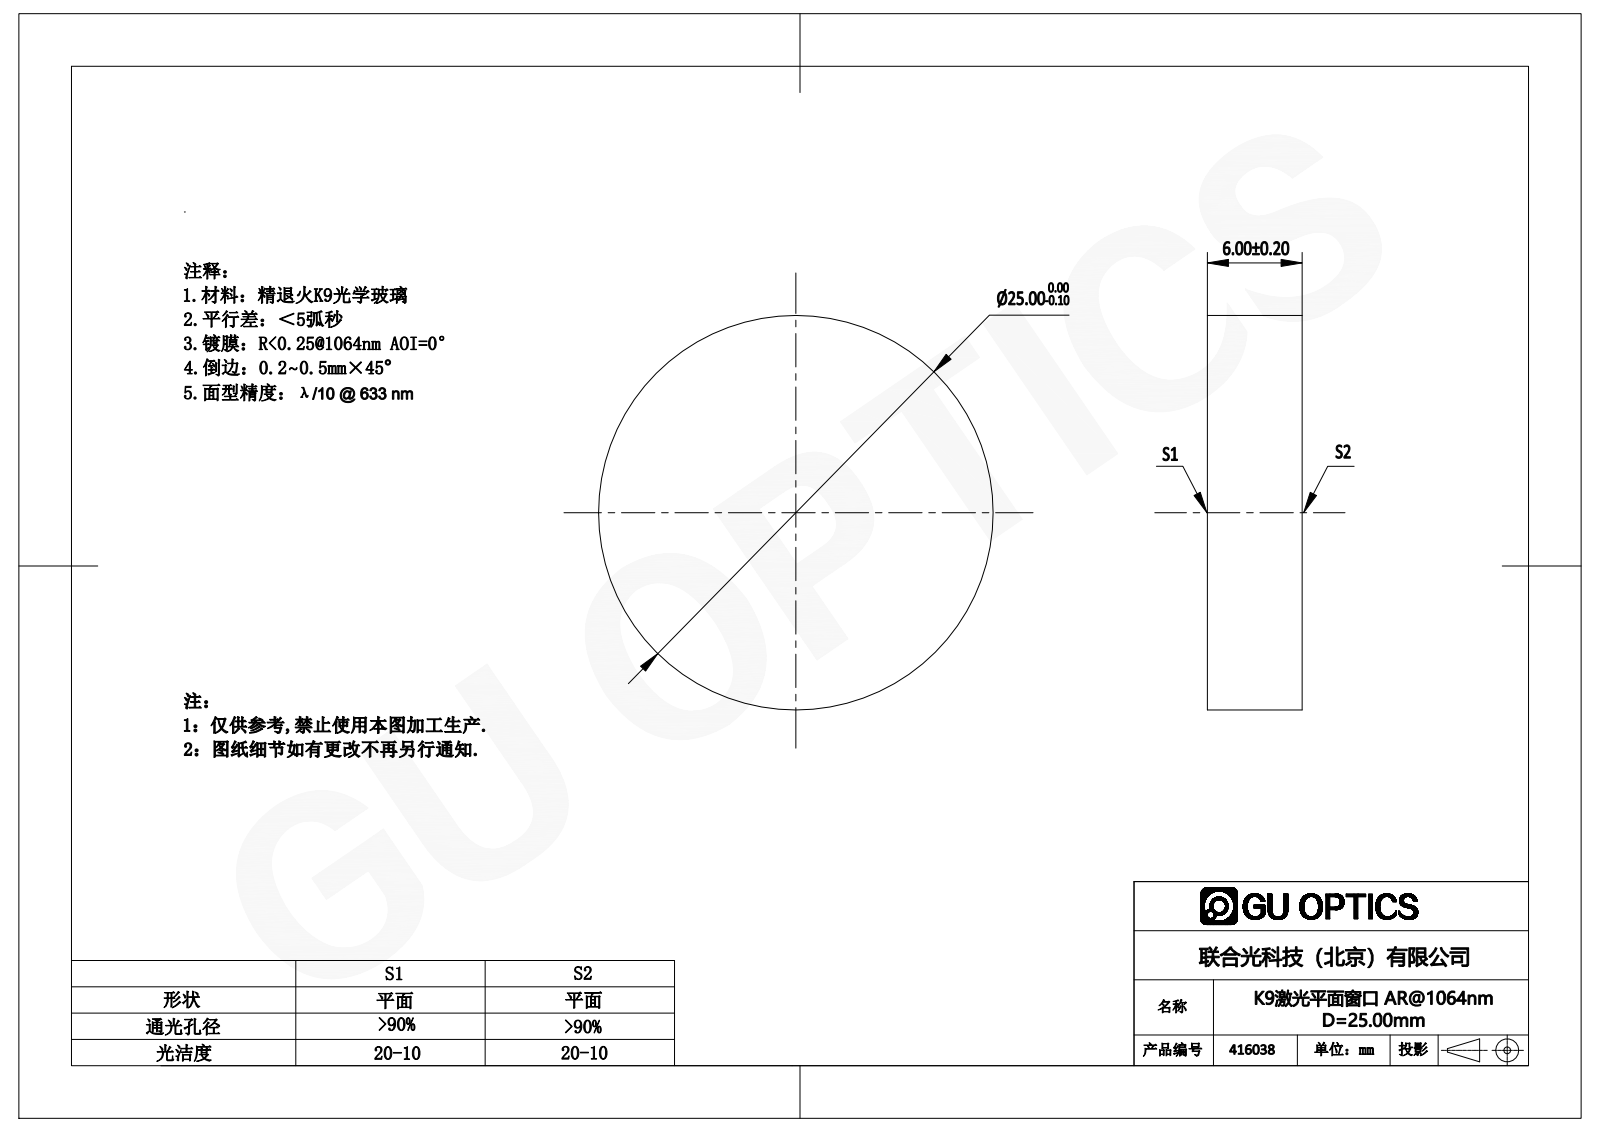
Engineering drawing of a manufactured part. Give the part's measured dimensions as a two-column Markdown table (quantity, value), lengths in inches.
| quantity | value |
| --- | --- |
| part name | 416005 |
| STEP written by | SolidWorks 2016 (CONFIG_CONTROL_DESIGN) |
| units | inches |
| bodies | 1 solid, 4 faces (2 planar, 2 cylindrical, 0 other) |
| overall size | 0.984 × 0.984 × 0.236 |
| volume | 0.18 in³ |
| surface area | 2.252 in² |
| round bosses / shafts (diameter × count) | 0.984 × 1 |
| main face-to-face distances | 0.236 |
